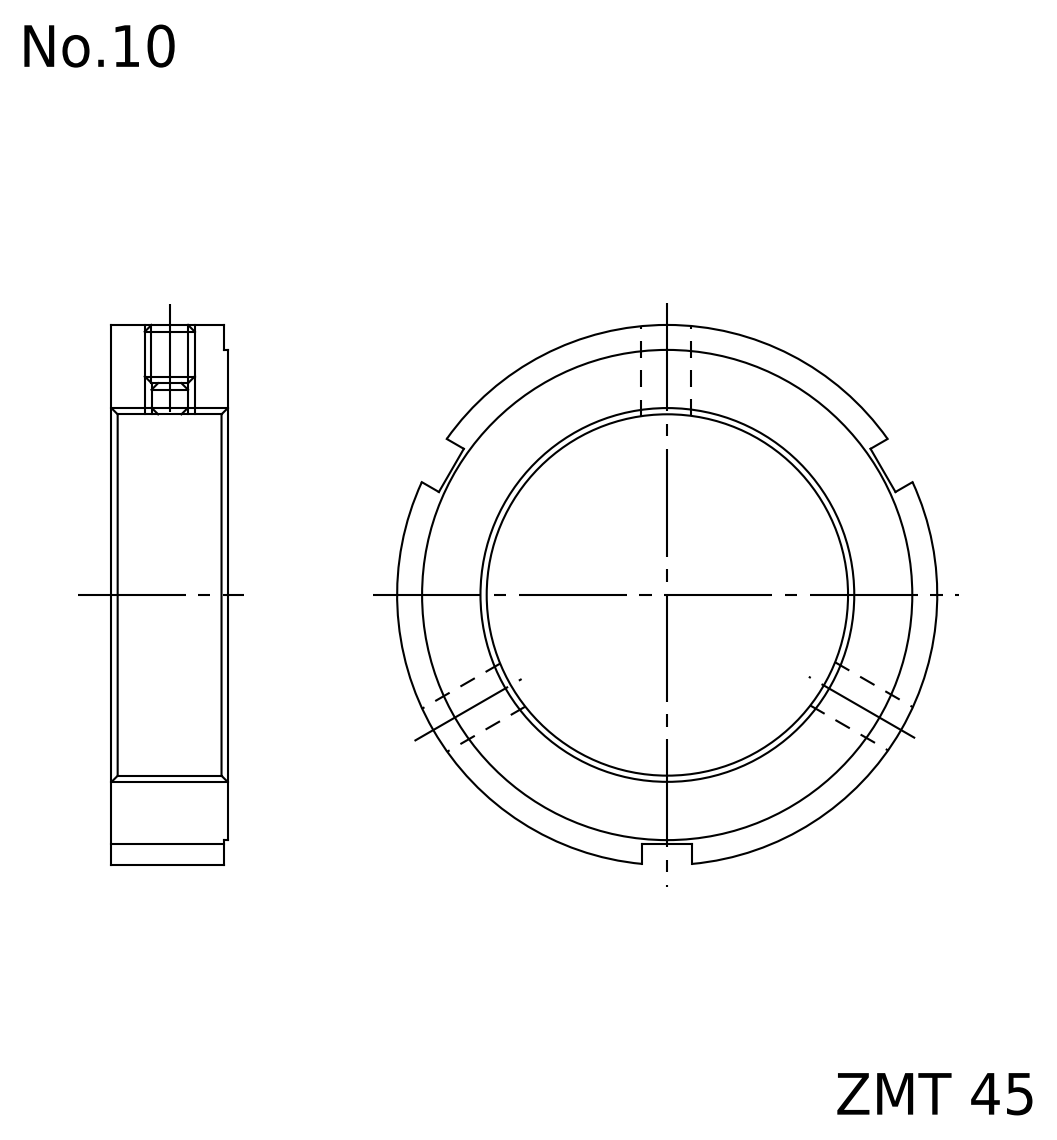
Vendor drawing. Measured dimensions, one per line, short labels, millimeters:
name: FKD ZMT 45
written by: Autodesk Inventor 2011 (AUTOMOTIVE_DESIGN)
unit: mm
bodies: 1 solid, 20 faces (12 planar, 8 cylindrical, 0 other)
size: 65 × 64.86 × 14
volume: 22 732 mm³; area: 8 737 mm²
holes: 3× ⌀4.92, 1× ⌀45
bosses: 1× ⌀65, 1× ⌀59
face distances: 14, 0.5, 13.5, 6
